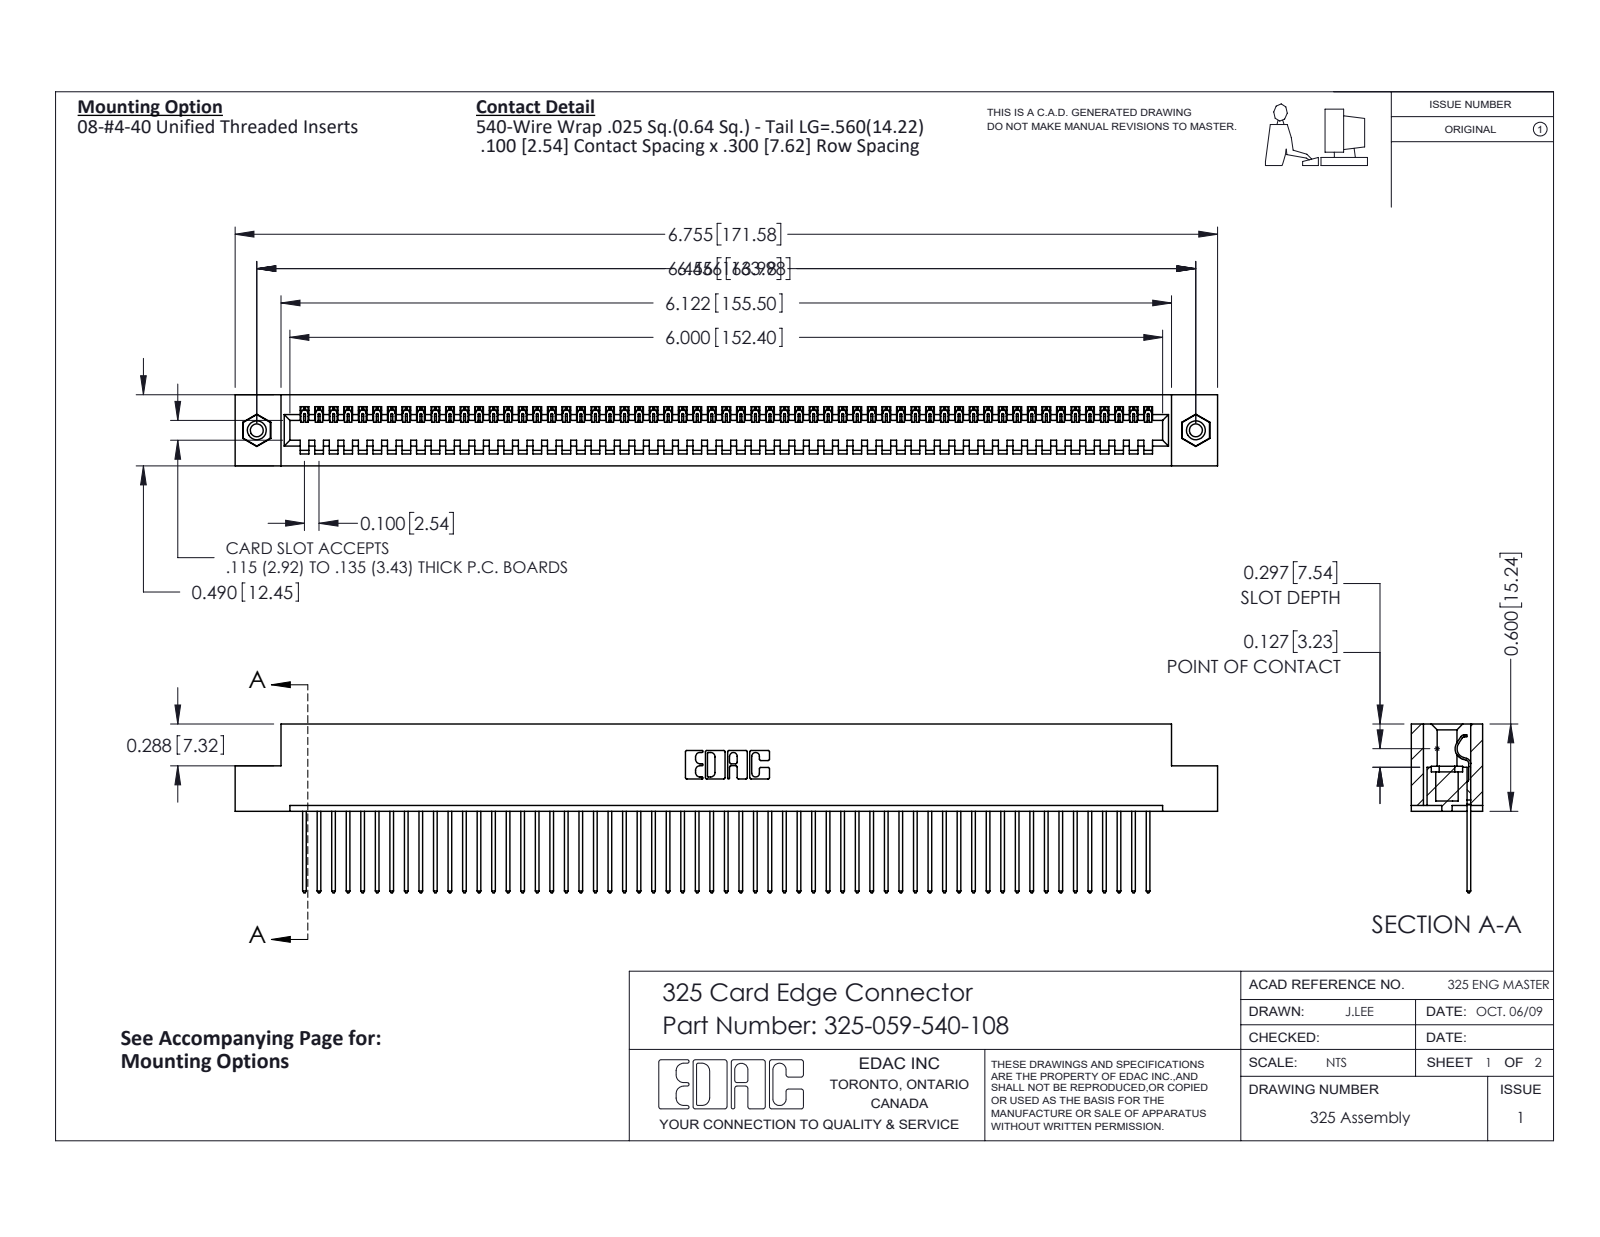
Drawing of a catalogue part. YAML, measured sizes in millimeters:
part_name: "325 Part_TI; 325-059-540-108; 325-292-001_325-293-140; 345-250-001_345-250-003-102"
step_written_by: "SolidWorks 2016 (CONFIG_CONTROL_DESIGN)"
units: millimeters
bodies: {solids: 62, faces: 3596, planar: 2580, cylindrical: 1000, other: 16}
overall_size: [171.6, 29.5, 12.4]
volume: 21990
surface_area: 24920
round_holes:
  - {diameter: 2.3, count: 2}
  - {diameter: 3.2, count: 2}
  - {diameter: 4.1, count: 2}
round_bosses_or_shafts:
  - {diameter: 3.9, count: 2}
partial_cylinders:
  - {radius: 0.2, count: 118}
  - {radius: 0.3, count: 118}
  - {radius: 0.3, count: 22}
  - {radius: 0.2, count: 6}
  - {radius: 0.8, count: 6}
  - {radius: 0.7, count: 3}
  - {radius: 0.4, count: 1}
  - {radius: 0.6, count: 1}
face_to_face_distances: [2.1, 10.3, 7.6, 12.4, 2.7, 9.7, 0.6, 8.3, 14.2, 6.7]
hole_center_spacings: [164]
